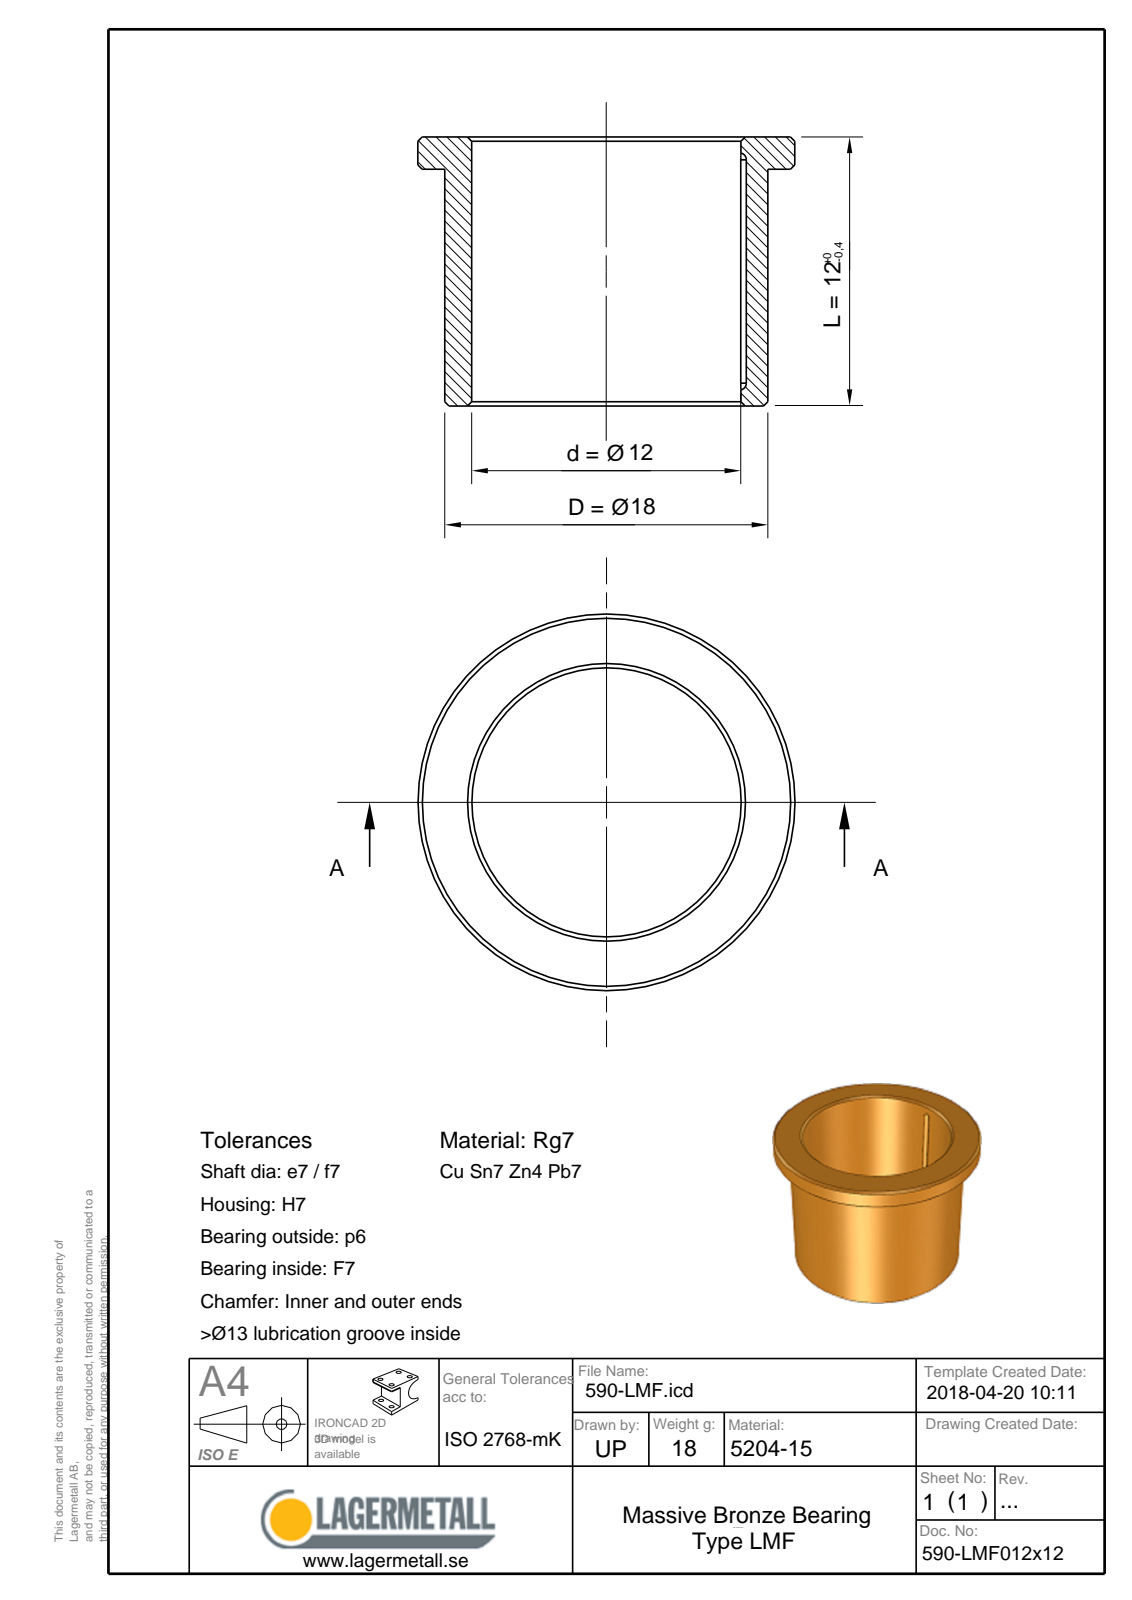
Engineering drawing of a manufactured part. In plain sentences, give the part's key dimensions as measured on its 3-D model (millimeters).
The part is named "590-LMF012x12". Its 3-D file was written by "Spatial InterOp 3D (CONFIG_CONTROL_DESIGN)". It is 1 solid with 11 faces: 3 planar, 3 cylindrical and 5 other. Overall it measures 22 by 22 by 12 millimeters. Its volume is 2 040 cubic millimeters and its surface area 1 623 square millimeters. Round holes: 1 of diameter 12. Round bosses or shafts: 1 of diameter 22, 1 of diameter 18. The main face-to-face distances are 12, 9, 3.
